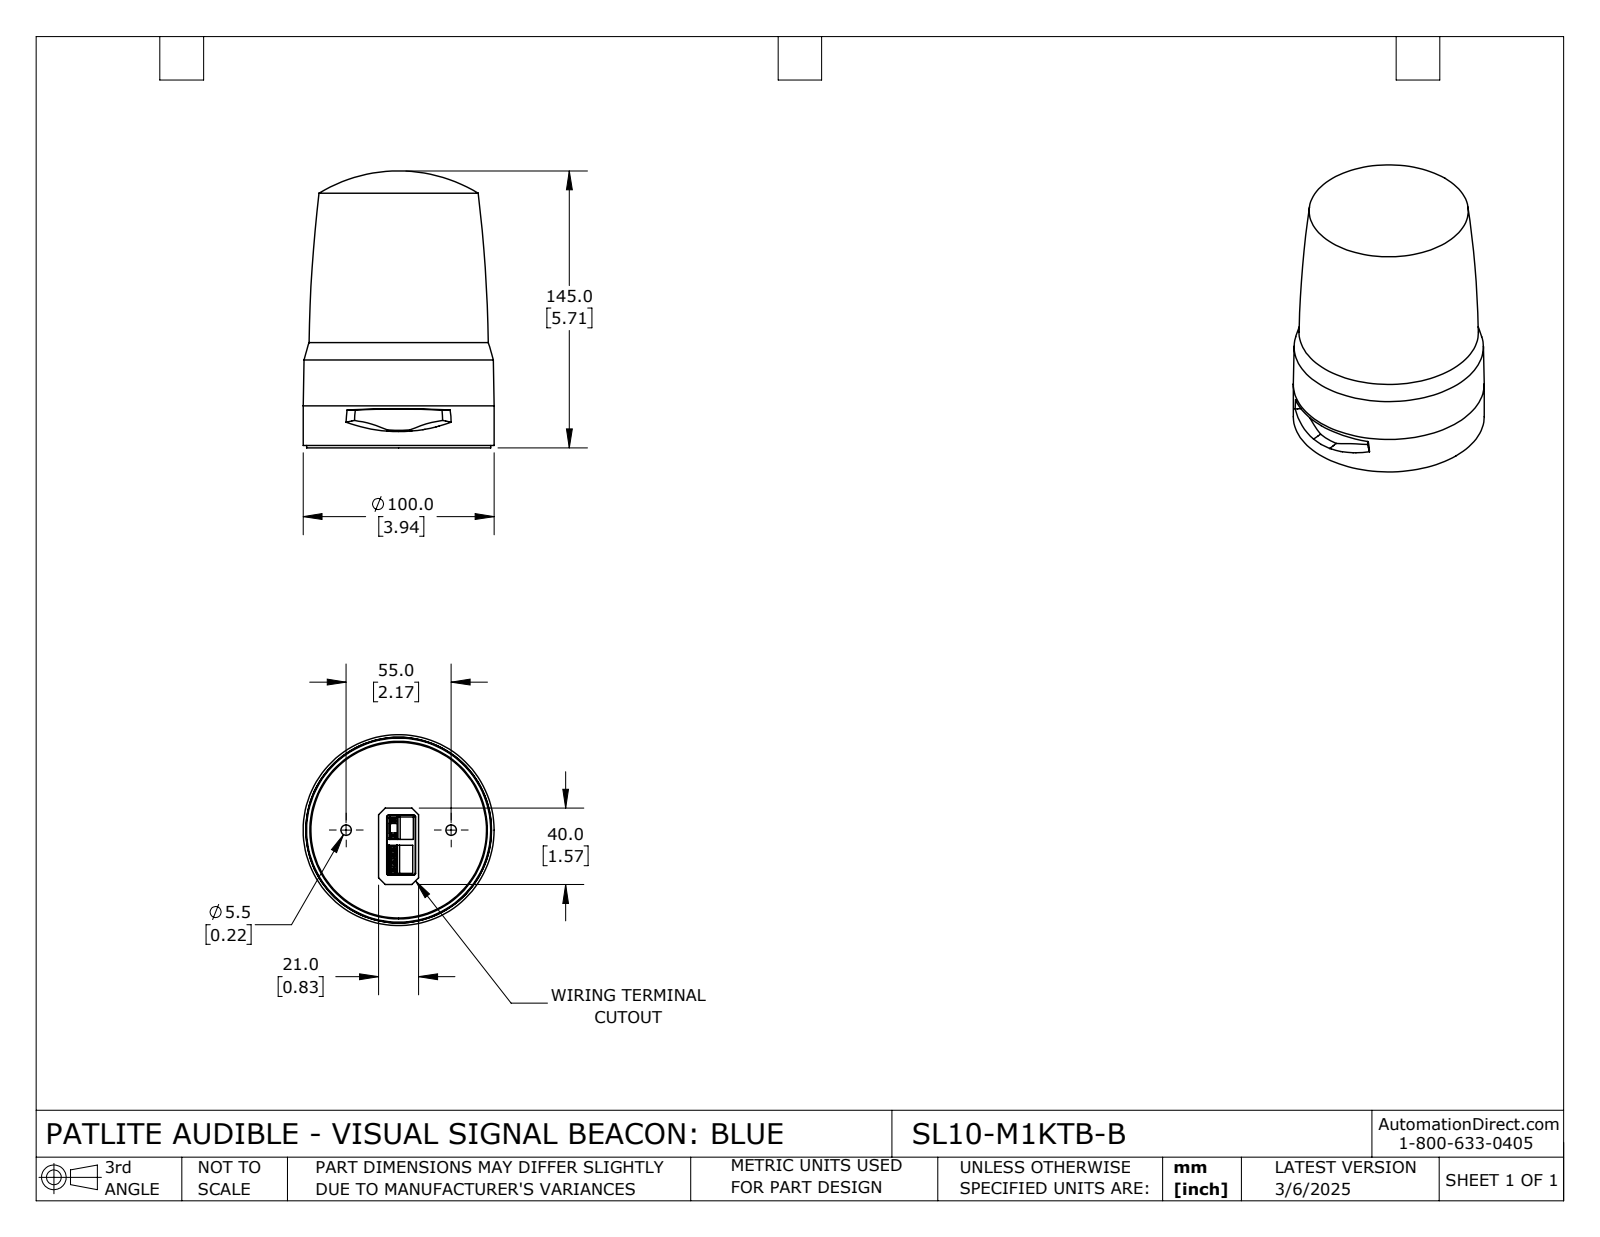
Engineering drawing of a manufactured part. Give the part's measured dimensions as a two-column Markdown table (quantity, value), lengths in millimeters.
| quantity | value |
| --- | --- |
| part name | SL10-M1KTB-B |
| STEP written by | SolidWorks 2024 (CONFIG_CONTROL_DESIGN) |
| units | millimeters |
| bodies | 2 solids, 275 faces (174 planar, 31 cylindrical, 70 other) |
| overall size | 145 × 100 × 100 |
| volume | 875 277 mm³ |
| surface area | 79 857 mm² |
| round holes (diameter × count) | 5.5 × 2, 13 × 2, 93 × 1 |
| round bosses / shafts (diameter × count) | 100 × 1, 96.4 × 1, 94.5 × 1, 93.2 × 1, 92 × 1 |
| partial cylindrical surfaces (radius × count) | 1 × 4, 0.3 × 2, 44.75 × 1, 45 × 1 |
| main face-to-face distances | 6.3, 18.2, 11.9, 5.6, 12.6, 5.1, 0.4, 4.7, 1.2, 17 |
| hole center spacings | 27.5, 55 |
